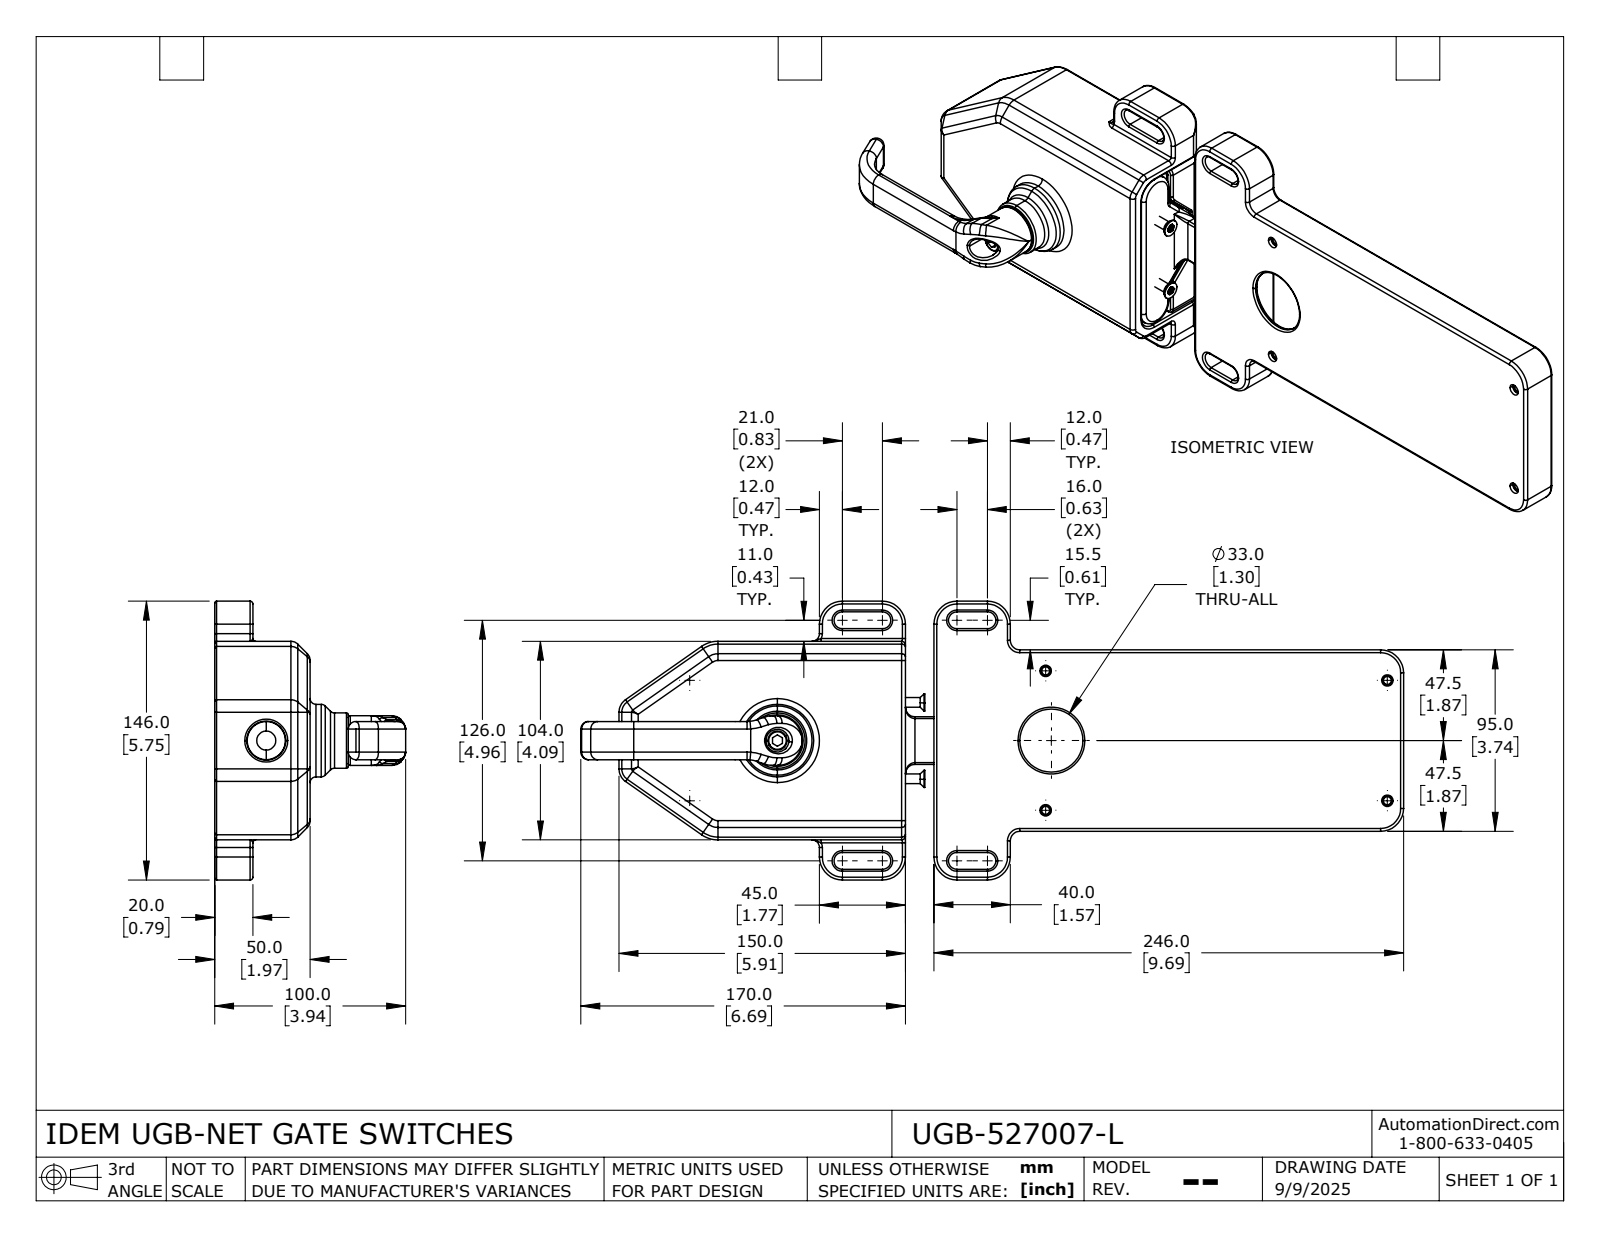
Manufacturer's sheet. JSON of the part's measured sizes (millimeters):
{"part_name": "527007-L", "step_written_by": "SolidWorks 2024 (AUTOMOTIVE_DESIGN)", "units": "millimeters", "bodies": {"solids": 15, "faces": 2006, "planar": 388, "cylindrical": 812, "other": 806}, "overall_size": [431, 146, 100], "volume_mm3": 458327, "surface_area_mm2": 235941, "round_holes": [[4.2, 10], [5.5, 4], [6, 4], [3.3, 2], [10.5, 2], [4, 1], [4.5, 1], [6.3, 1], [6.66, 1], [6.8, 1], [12, 1], [14.2, 1]], "round_bosses_or_shafts": [[6, 5], [11, 4], [20, 2], [10, 2], [9, 2], [7, 2], [38, 1], [29, 1]], "partial_cylinders_radius": [[1, 277], [2, 88], [3, 26], [5, 26], [1.5, 21], [0.8, 19], [0.5, 16], [0.45, 12]], "face_to_face_distances": [2.5, 16.5, 3.5, 19, 1, 46.5, 32.5, 43, 30, 49], "hole_center_spacings": [20.62, 36.62, 39.91, 55.75, 63, 67.68, 83.41, 92.58]}
